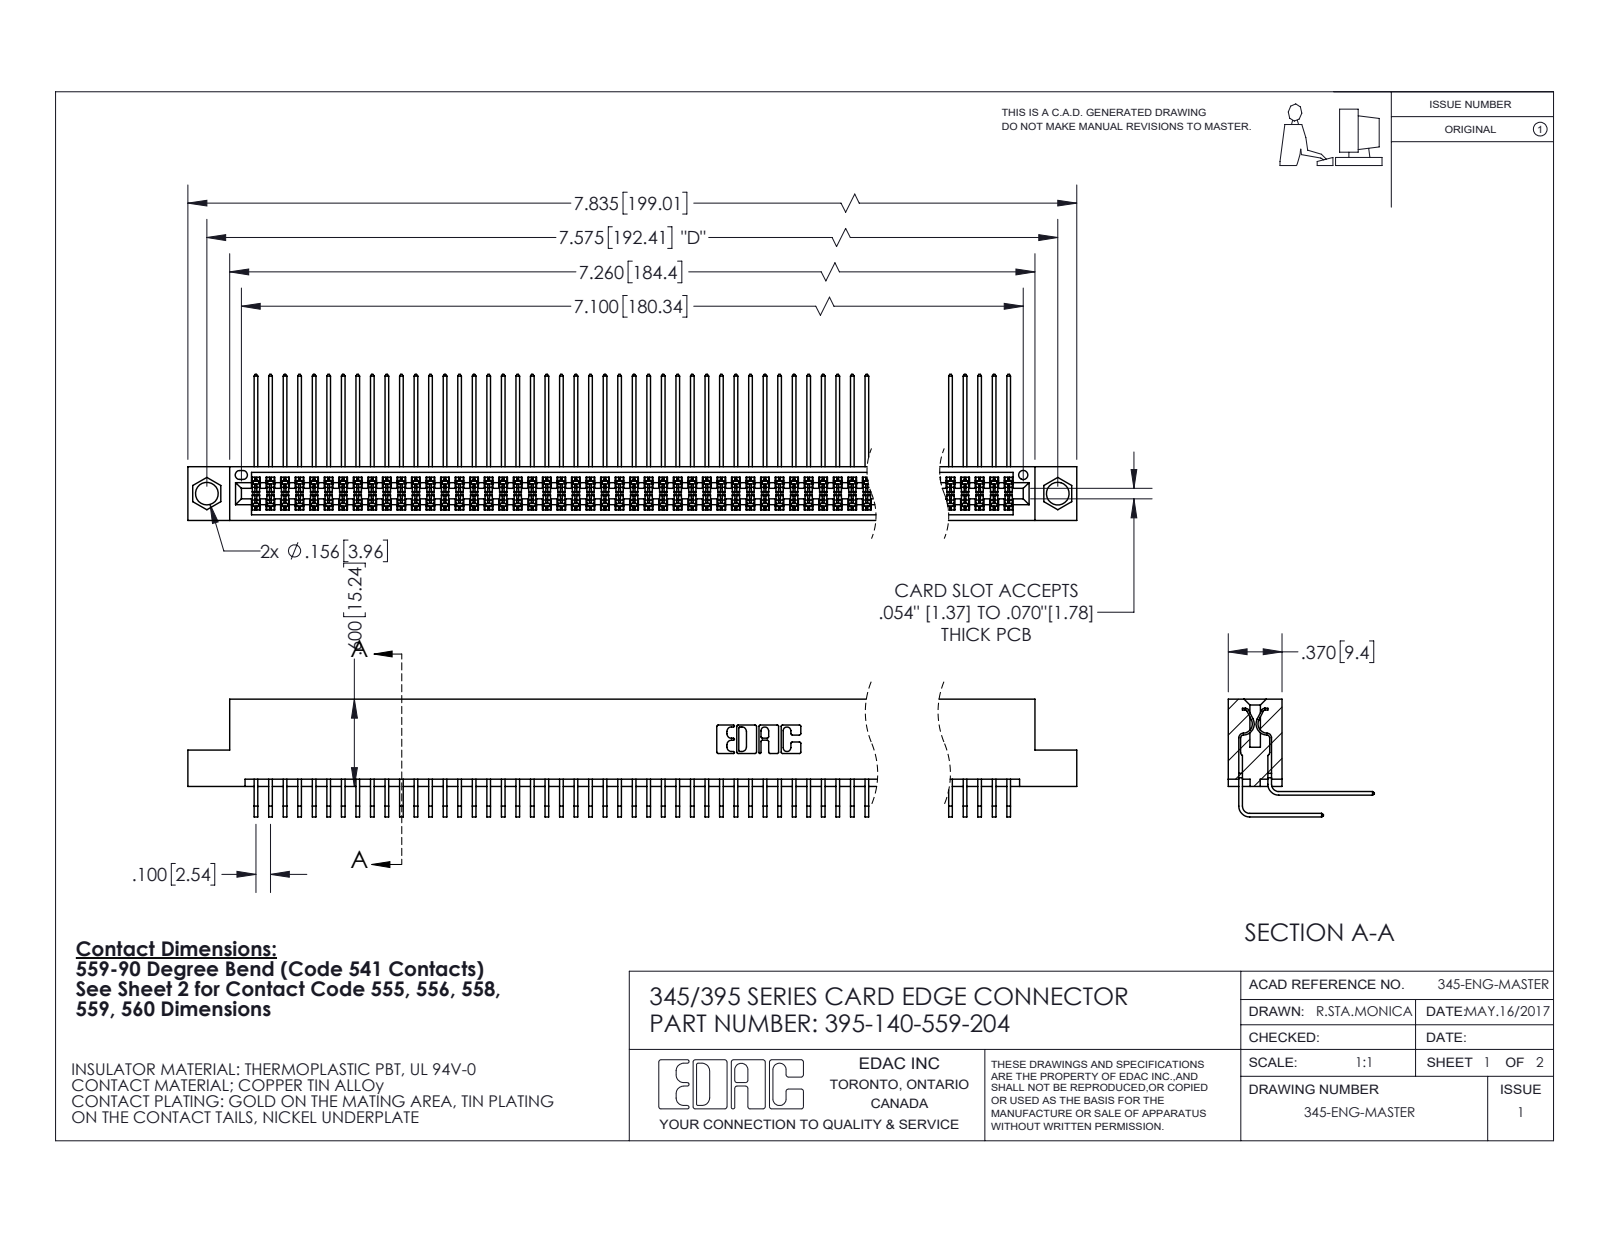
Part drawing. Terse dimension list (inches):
name: 345 Part_Flush Mounting Lugs - 0.156 Dia-TI; 395-140-559-204; 345-292-001_558 559 Tail - 1; 345-292-001_559 Tail - 2
written by: SolidWorks 2020 (CONFIG_CONTROL_DESIGN)
unit: in
bodies: 141 solids, 7420 faces (4994 planar, 2426 cylindrical, 0 other)
size: 7.835 × 1.005 × 0.809
volume: 1.238 in³; area: 52.99 in²
holes: 2× ⌀0.156, 1× ⌀0.064
rounds: 210× R0.006, 22× R0.01, 6× R0.007, 6× R0.031, 3× R0.026, 2× R0.014, 2× R0.019, 2× R0.022
face distances: 0.072, 0.298, 0.2, 0.37, 0.098, 0.272, 0.025, 0.225, 0.175, 0.15
hole spacings: 0.27, 7.339, 7.575
